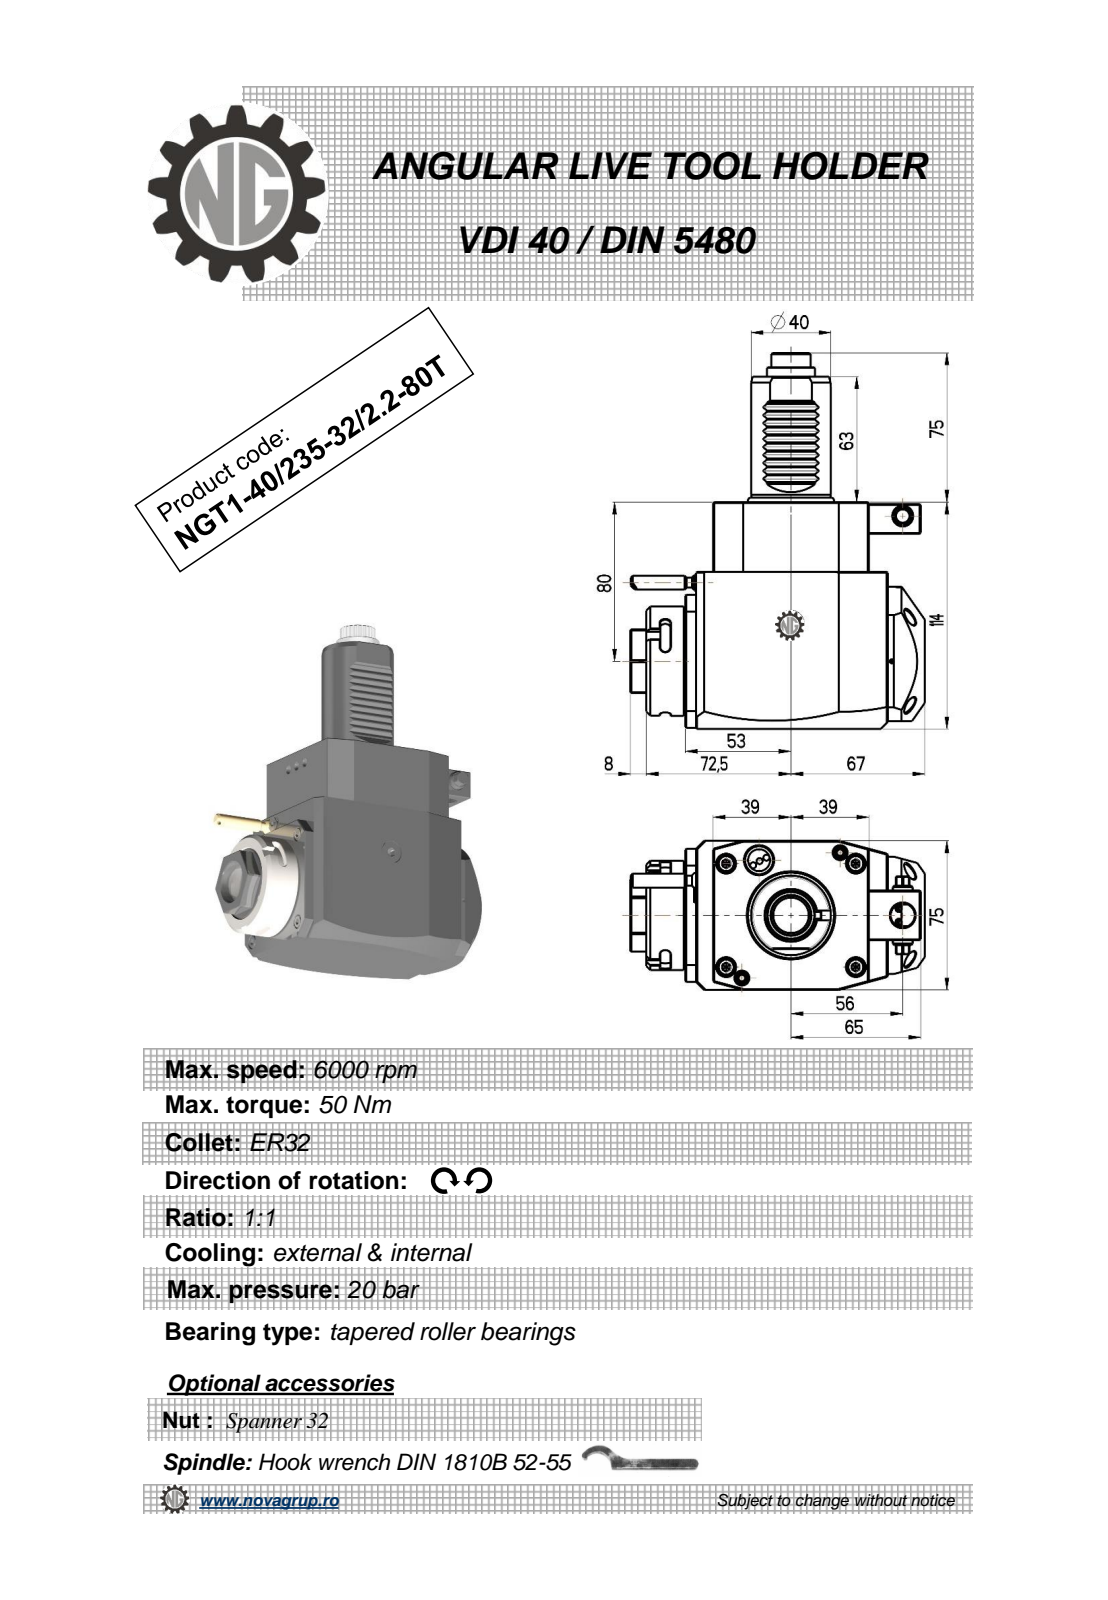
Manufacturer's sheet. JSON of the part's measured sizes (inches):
{"part_name": "NGT1_40_235_32_1_2_80T", "step_written_by": "PRO/ENGINEER BY PARAMETRIC TECHNOLOGY CORPORATION, 2010280 (CONFIG_CONTROL_DESIGN)", "units": "inches", "bodies": {"solids": 1, "faces": 458, "planar": 192, "cylindrical": 172, "other": 94}, "overall_size": [7.441, 5.807, 2.953], "volume_in3": 58.93, "surface_area_in2": 111.7, "round_holes": [[0.098, 1], [0.118, 1], [0.374, 1], [0.472, 1], [0.906, 1]], "round_bosses_or_shafts": [[0.315, 2], [2.165, 1], [1.89, 1], [1.575, 1], [0.945, 1], [0.394, 1], [0.276, 1], [0.197, 1]], "partial_cylinders_radius": [[0.082, 48], [0.012, 10], [0.098, 6], [7.087, 2], [0.152, 1], [0.167, 1], [0.357, 1], [0.391, 1]], "face_to_face_distances": [2.953, 4.488, 0.551, 3.622, 3.071, 3.11, 0.984, 0.768, 1.319, 4.39], "hole_center_spacings": [1.436, 1.701, 2.815]}
